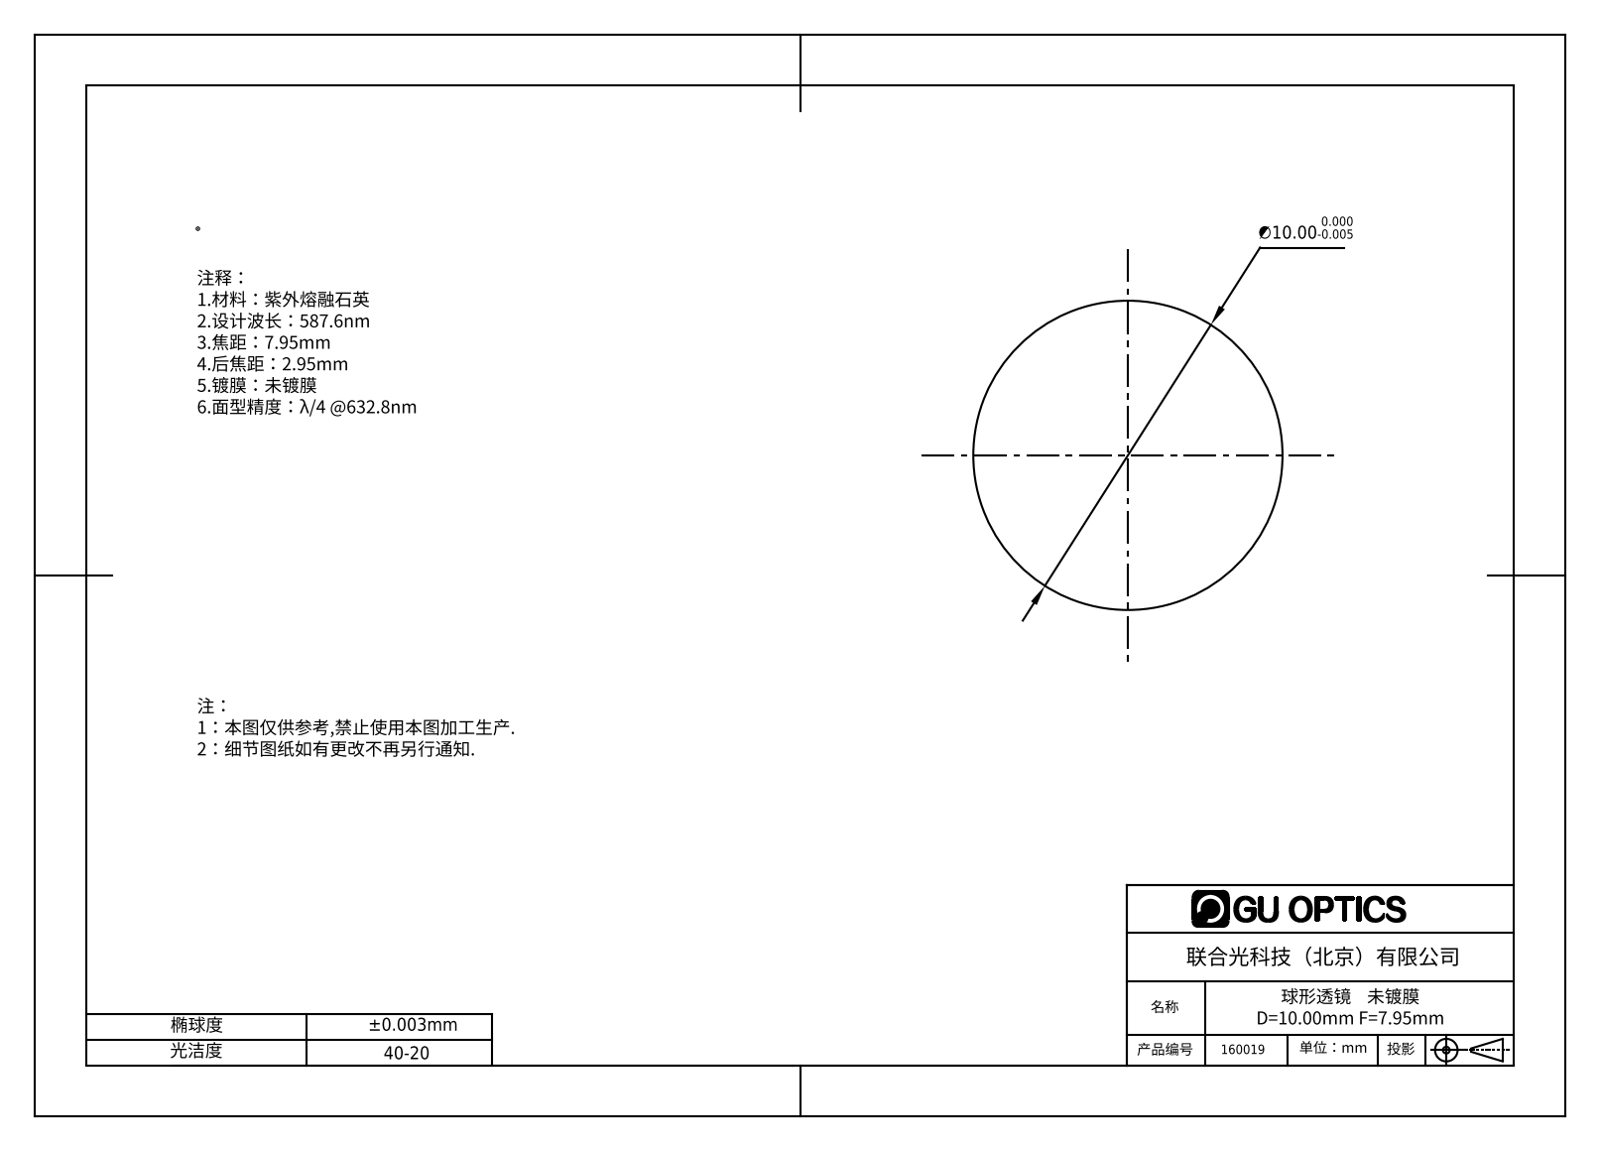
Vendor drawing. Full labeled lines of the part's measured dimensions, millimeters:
Part name (STEP PRODUCT): 160009
STEP written by: SolidWorks 2016 (CONFIG_CONTROL_DESIGN)
Units: millimetres
Bodies: 1 solid, 2 faces (0 planar, 0 cylindrical, 2 other)
Overall size (bounding box): 10 × 10 × 10
Volume: 524 mm³ · Surface area: 314 mm²
